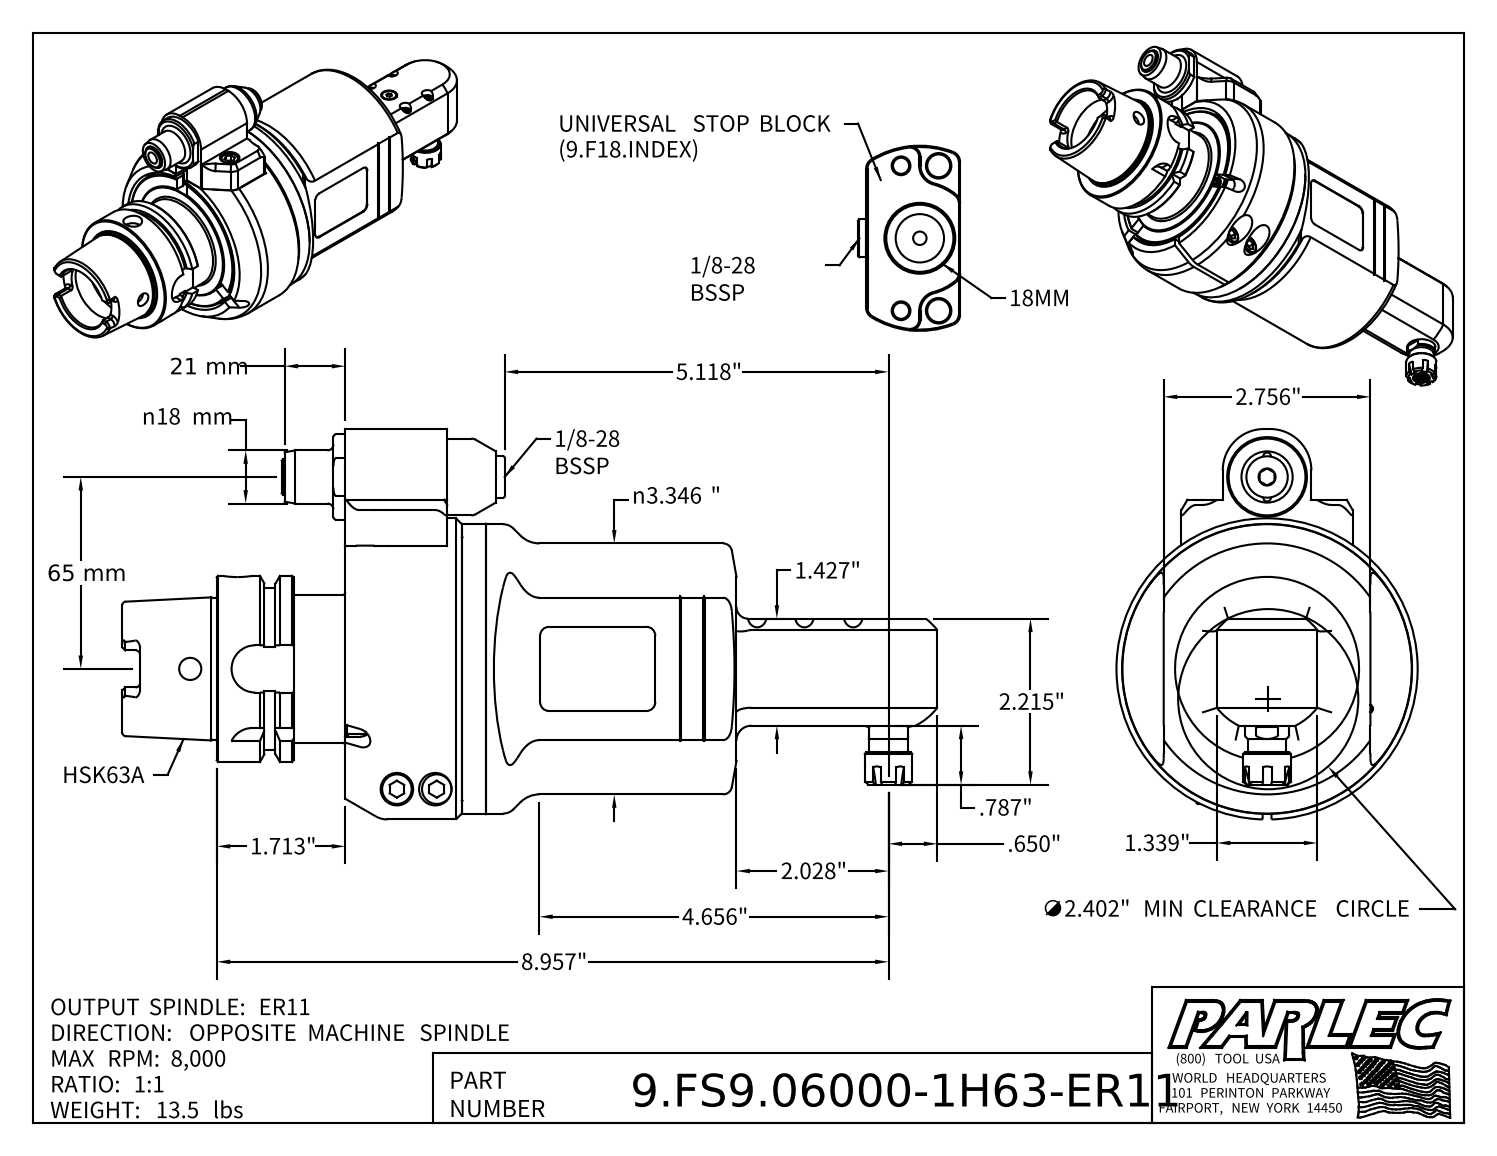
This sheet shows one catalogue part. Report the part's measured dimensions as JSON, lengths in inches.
{"part_name": "9.FS9.06000-1H63-ER11; 9_FS9_06000_E11; 9_GA1_566_2 (EVO, Type 1, H63A, 65mm)", "step_written_by": "Autodesk Inventor 2022 (AUTOMOTIVE_DESIGN)", "units": "inches", "bodies": {"solids": 5, "faces": 624, "planar": 318, "cylindrical": 153, "other": 153}, "overall_size": [10.866, 5.206, 4.016], "volume_in3": 64.63, "surface_area_in2": 223.3, "round_holes": [[0.236, 6], [0.165, 3], [0.102, 2], [0.197, 2], [0.295, 2], [0.335, 2], [0.409, 2], [0.433, 2], [0.492, 2], [0.098, 1], [0.118, 1], [0.256, 1]], "round_bosses_or_shafts": [[0.217, 6], [0.394, 4], [0.236, 4], [0.315, 3], [0.709, 2], [0.098, 2], [4.016, 1], [3.866, 1]], "partial_cylinders_radius": [[0.079, 8], [0.059, 6], [1.181, 6], [0.157, 5], [0.197, 5], [0.113, 4], [0.118, 4], [0.315, 4]], "face_to_face_distances": [1.26, 2.047, 1.22, 0.335, 0.709, 1.339, 1.024, 0.039, 1.555, 0.02], "hole_center_spacings": [1.043, 0.276, 0.523, 0.63, 0.651, 0.703, 0.804, 0.848]}
